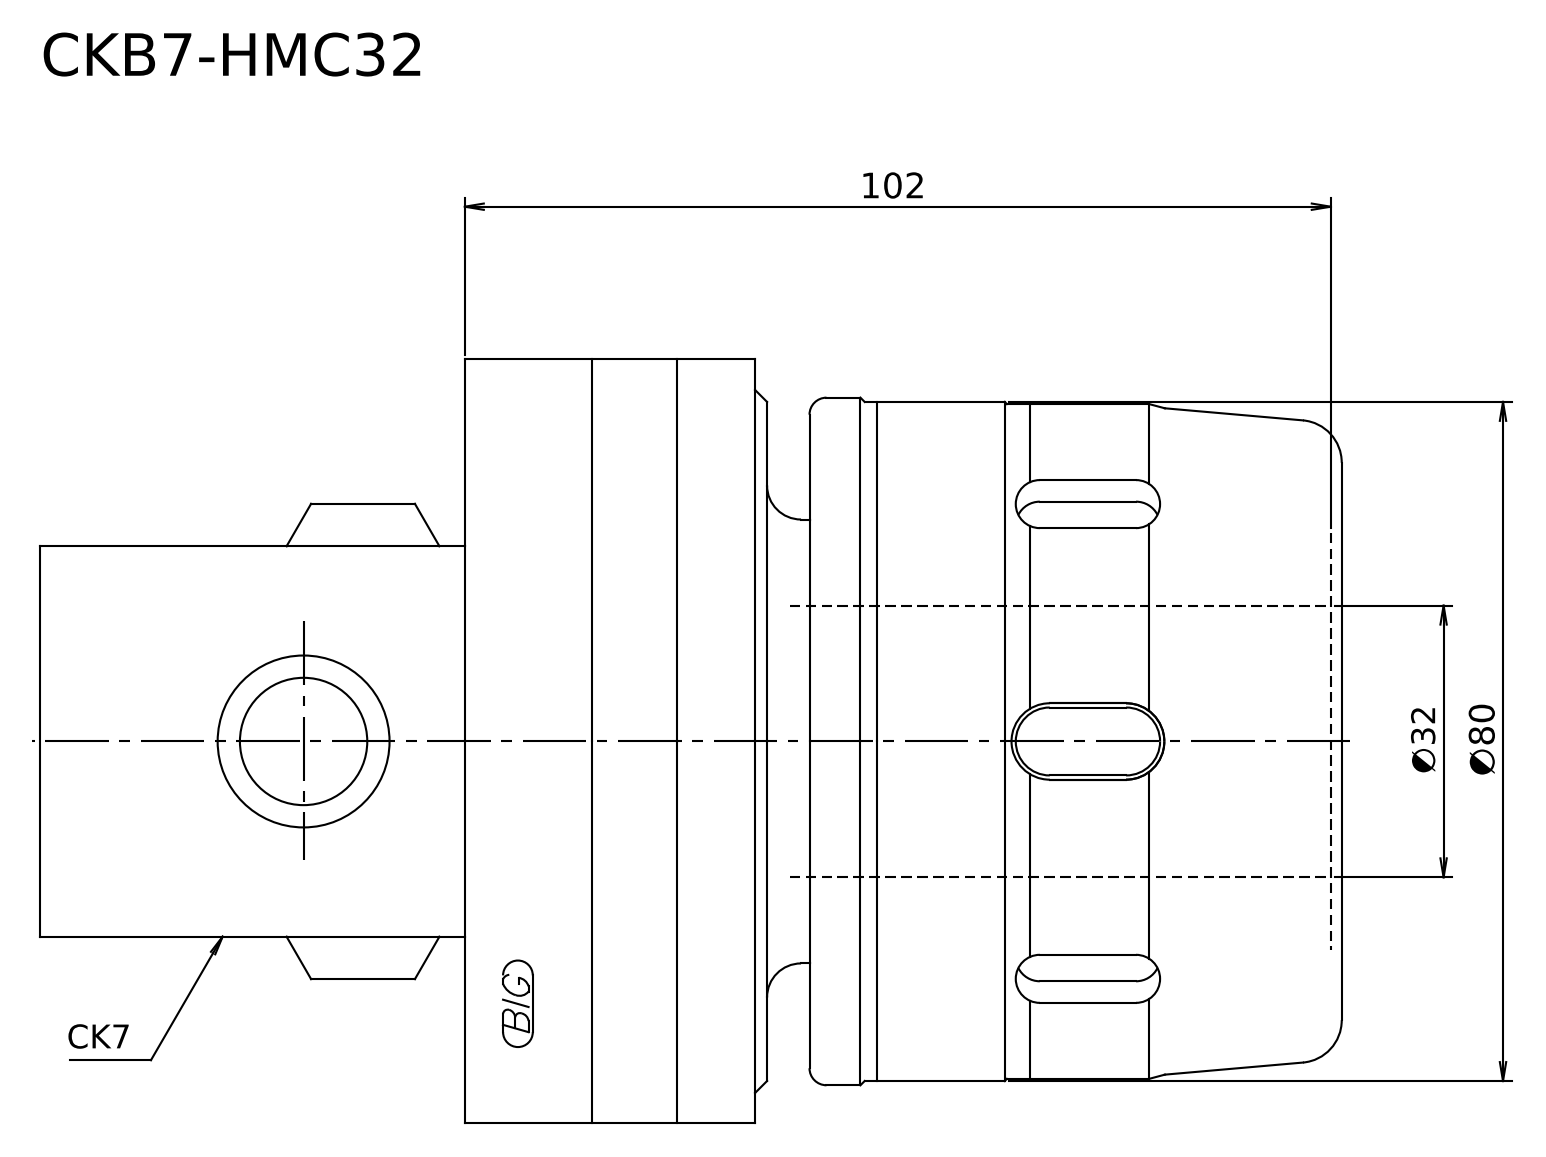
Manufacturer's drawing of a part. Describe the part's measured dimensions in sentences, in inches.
Its 3-D file was written by "Kubotek KeyCreator V8.5.1 (14335) (CONFIG_CONTROL_DESIGN)". It is 1 solid with 16 faces: 5 planar, 5 cylindrical and 6 other. Overall it measures 4.067 by 3.543 by 3.543 inches. Its volume is 33.14 cubic inches and its surface area 68.04 square inches. Round bosses or shafts: 1 of diameter 3.543, 1 of diameter 3.189, 1 of diameter 3.15, 1 of diameter 3.13, 1 of diameter 2.059. The main face-to-face distances are 4.067, 2.469, 1.598, 2.665, 0.197, 1.402, 2.72, 0.252, 0.055, 1.346.
